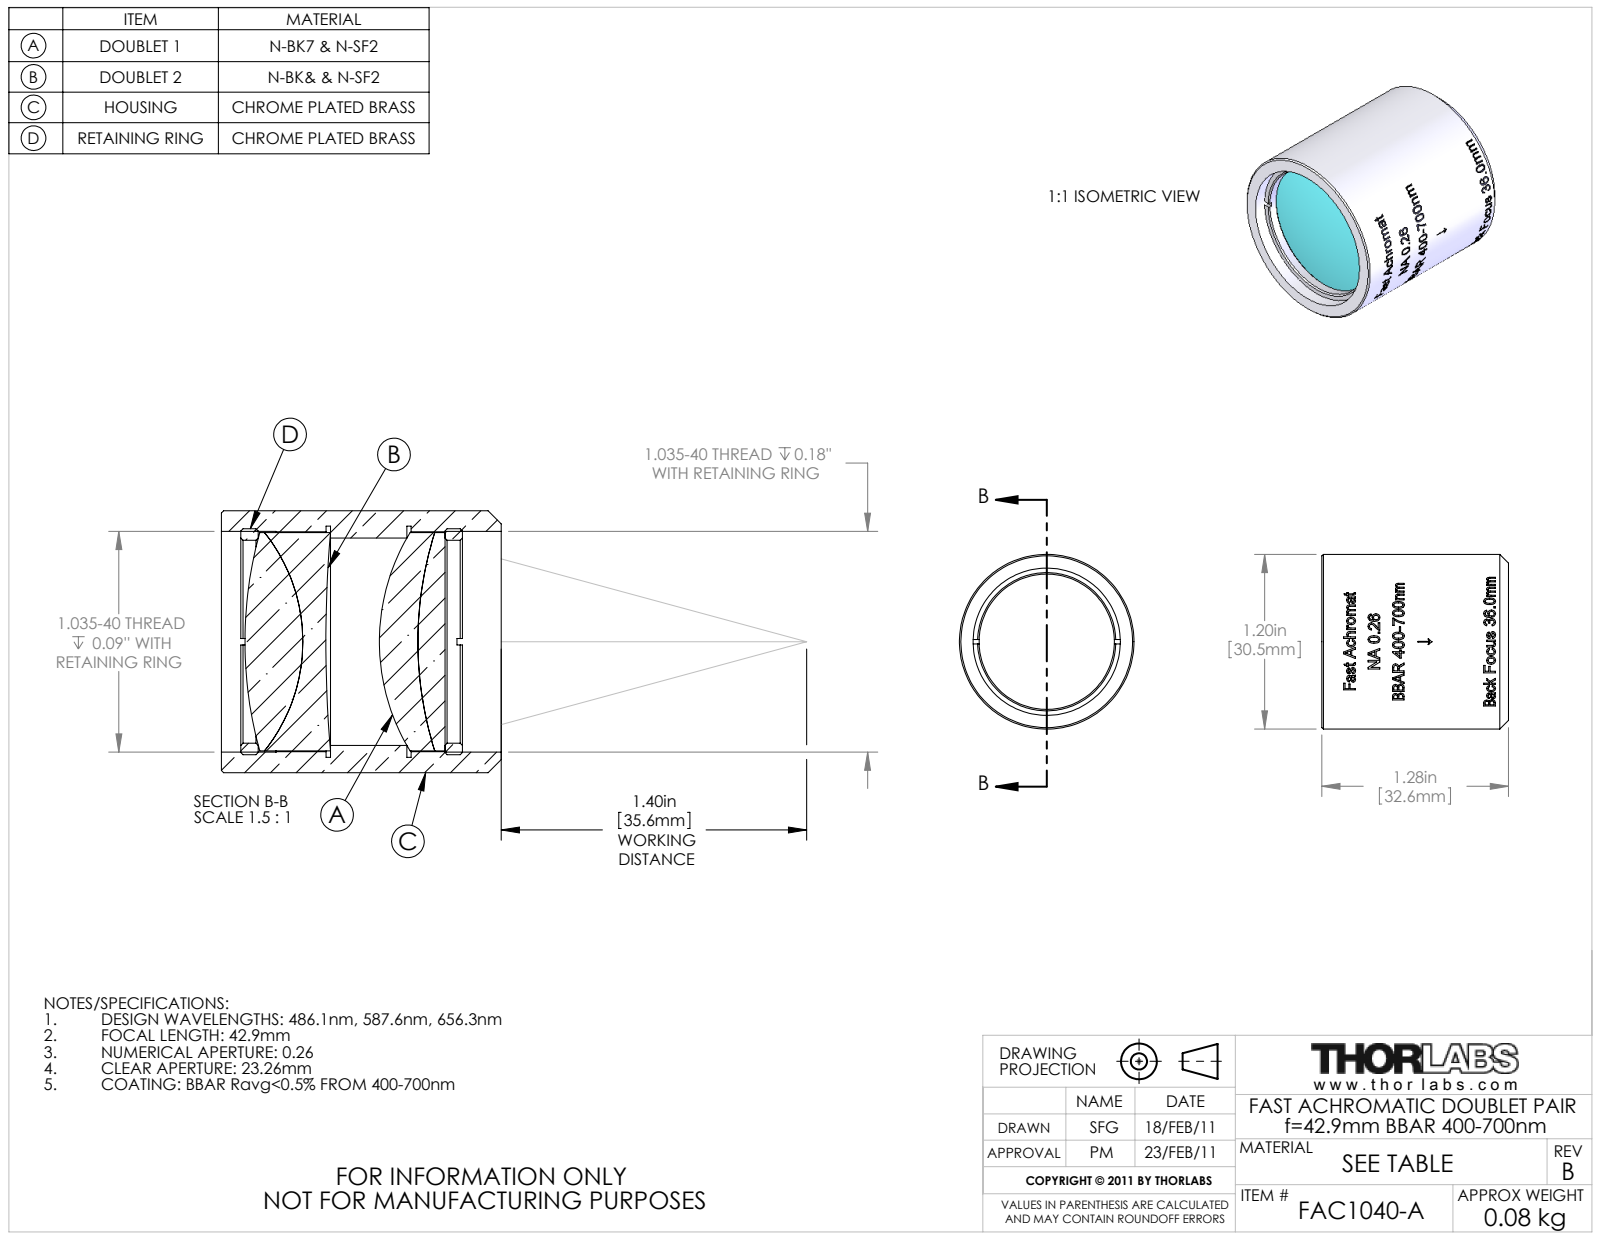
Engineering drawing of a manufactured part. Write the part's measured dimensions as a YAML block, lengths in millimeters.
part_name: "20561-E0W"
step_written_by: "SolidWorks 2009 (AUTOMOTIVE_DESIGN)"
units: millimeters
bodies: {solids: 7, faces: 201, planar: 25, cylindrical: 138, other: 38}
overall_size: [32.6, 30.5, 30.5]
volume: 15200
surface_area: 12560
round_holes:
  - {diameter: 23.6, count: 1}
  - {diameter: 24.1, count: 1}
  - {diameter: 25.6, count: 1}
  - {diameter: 25.7, count: 1}
  - {diameter: 26.9, count: 1}
round_bosses_or_shafts:
  - {diameter: 30.5, count: 1}
  - {diameter: 26.3, count: 1}
  - {diameter: 25.4, count: 1}
face_to_face_distances: [26, 2, 23.8, 13.3, 12.7, 4.4, 8.9, 21.6, 0.5, 9.4]
